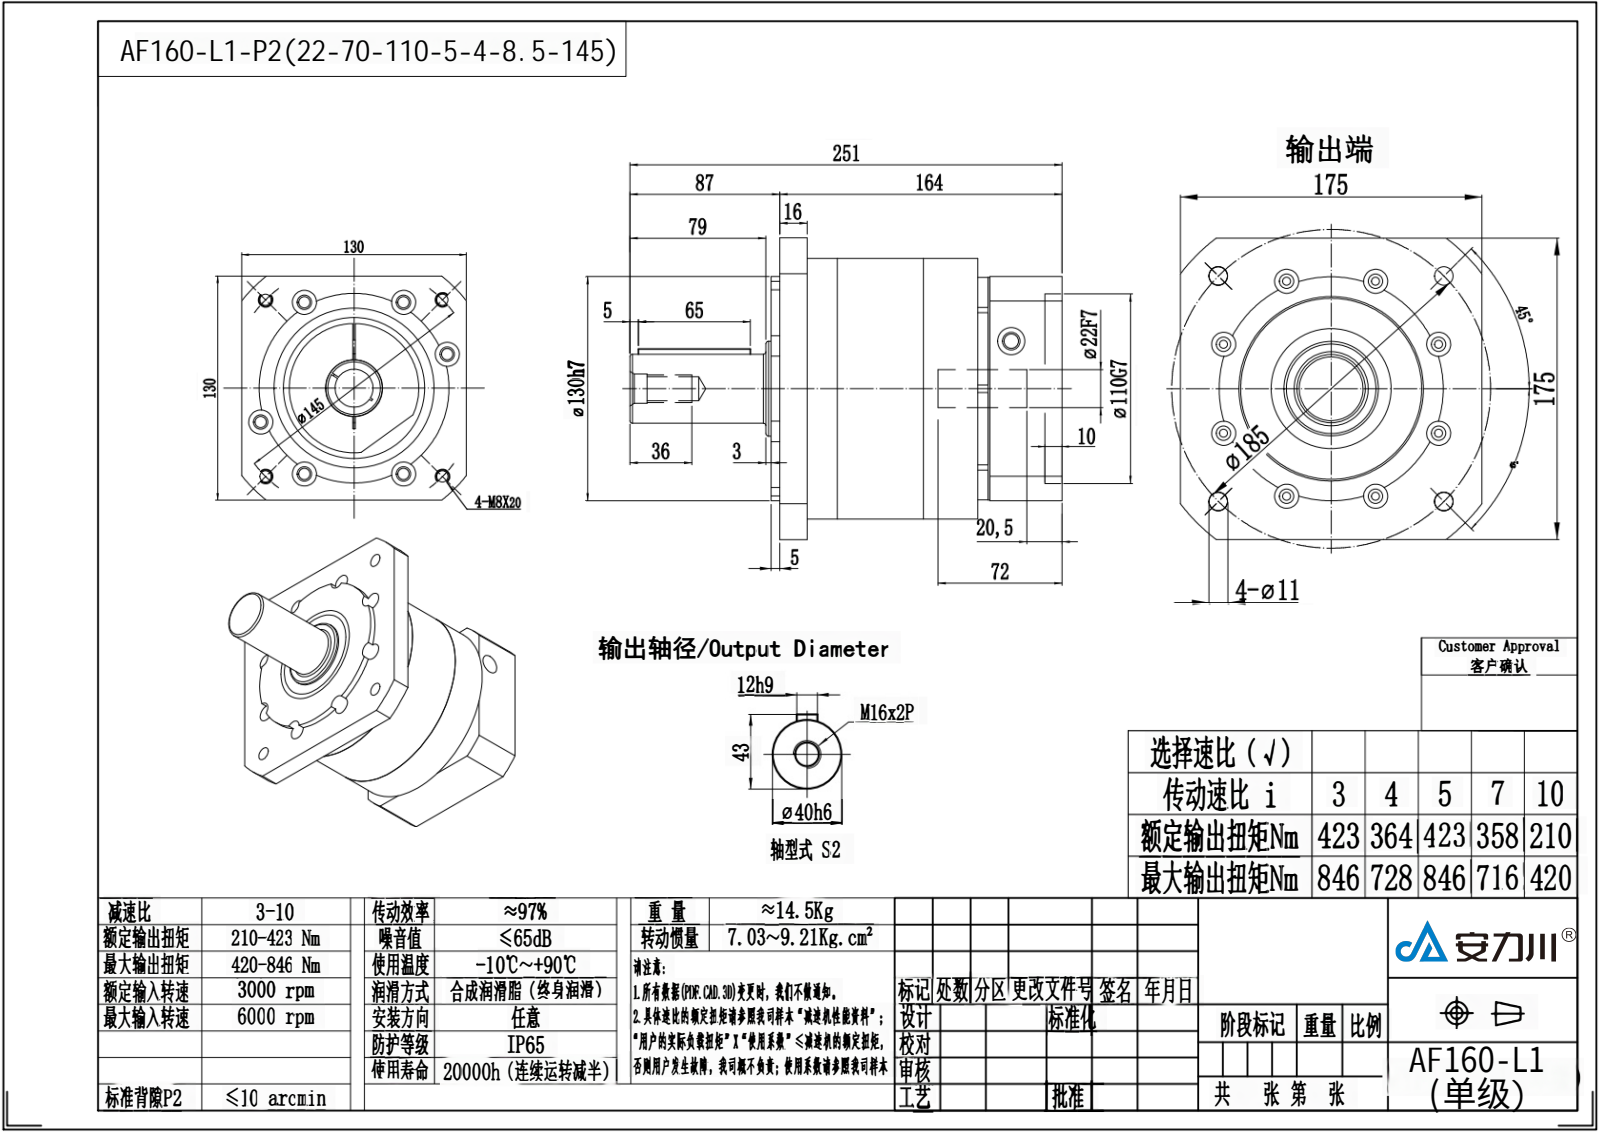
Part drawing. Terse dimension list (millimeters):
name: hexagon socket head cap screws gb_GB_FASTENER_SCREWS_HSHCS M8X12-N; plain parallel keys_GB_CONNECTING_PIECE_KEYS_CSK 12X63; MYA142输入太阳轮-28; MYA142锁紧环28 (+8 more)
written by: SolidWorks 2022 (CONFIG_CONTROL_DESIGN)
unit: mm
bodies: 41 solids, 1615 faces (549 planar, 389 cylindrical, 677 other)
size: 251 × 175 × 175
volume: 2 521 000 mm³; area: 420 974 mm²
holes: 16× ⌀14, 15× ⌀8.5, 8× ⌀6.68, 6× ⌀5.6, 4× ⌀6.8, 4× ⌀11, 1× ⌀10.5, 1× ⌀17, 1× ⌀28, 1× ⌀29, 1× ⌀50, 1× ⌀76.67
bosses: 14× ⌀13, 14× ⌀8, 9× ⌀10, 8× ⌀9.88, 8× ⌀6, 1× ⌀151, 1× ⌀129, 1× ⌀120
rounds: 8× R1, 8× R2, 3× R6, 1× R8.5, 1× R31, 1× R37.5, 1× R38, 1× R65
face distances: 50, 83.5, 33.5, 17.5, 38.5, 22.5, 121, 87.5, 37.5, 16
hole spacings: 134.12, 26.73, 75.99, 113.71, 51.66, 67.5, 69.25, 95.46
